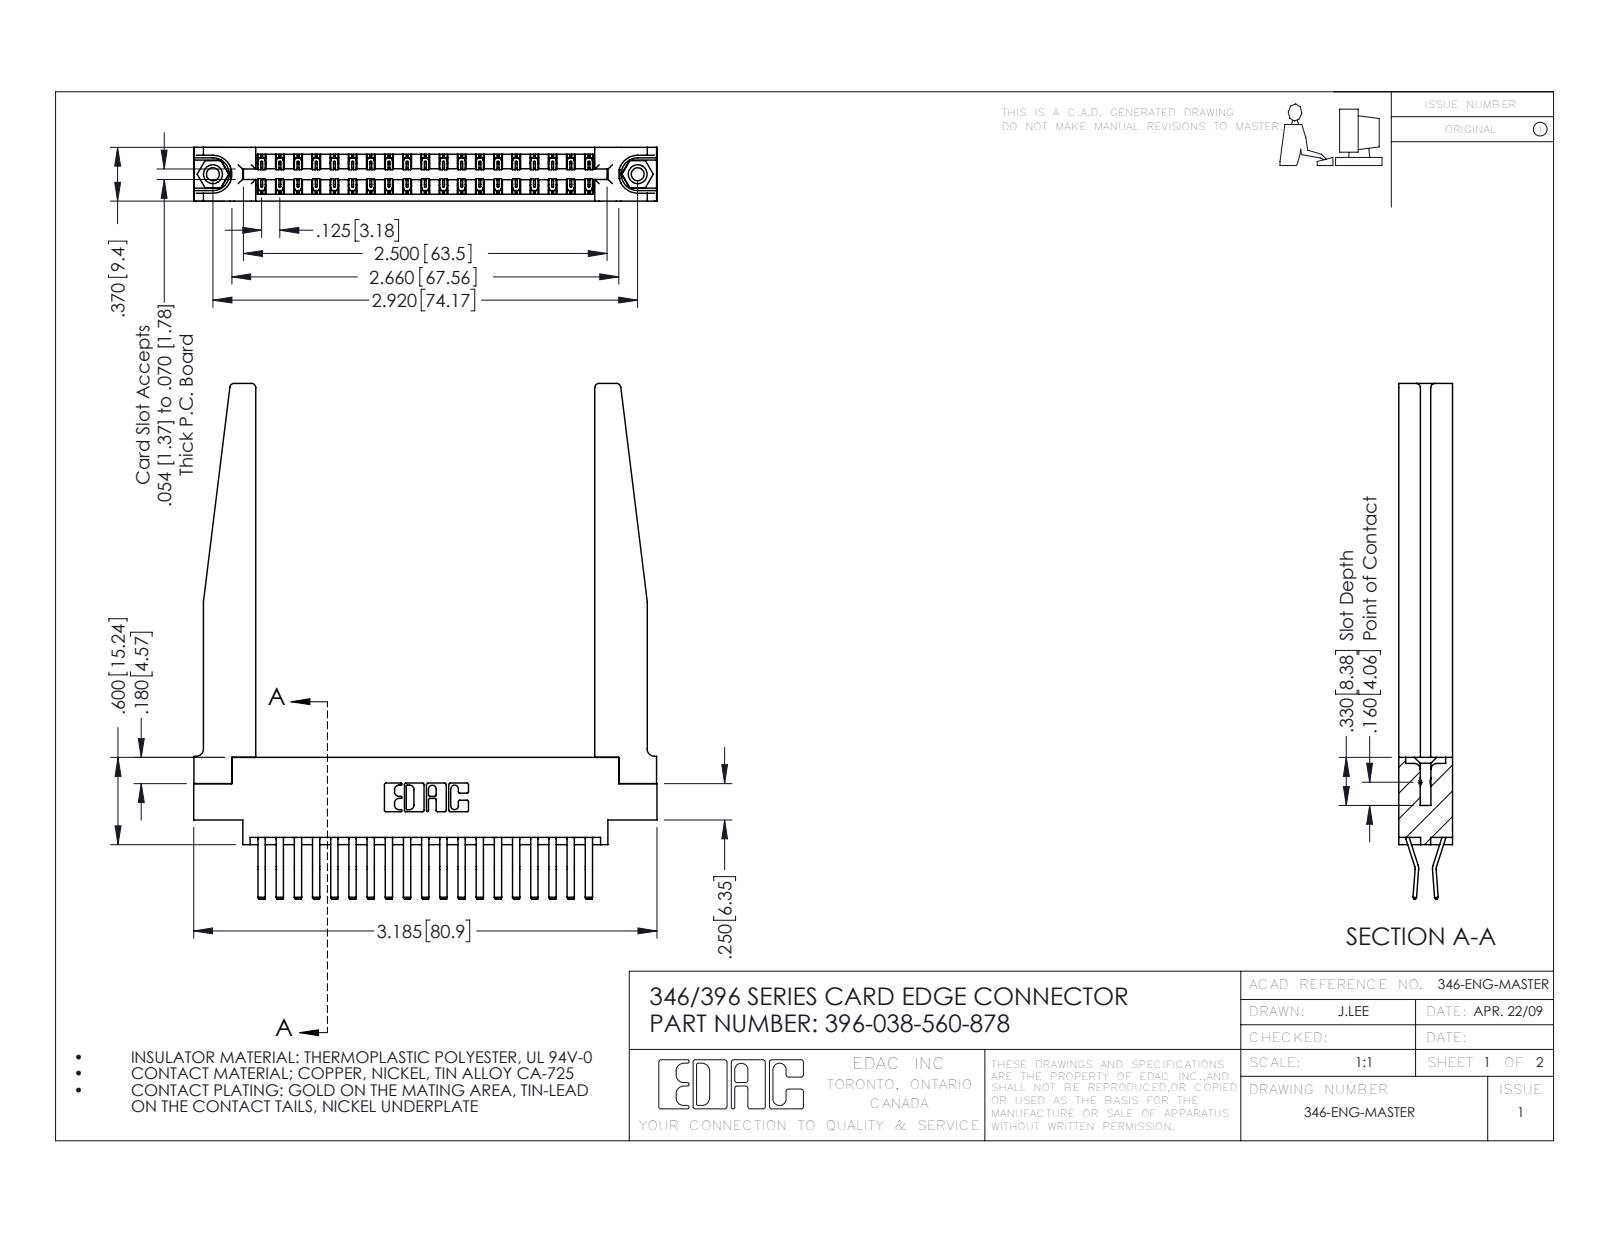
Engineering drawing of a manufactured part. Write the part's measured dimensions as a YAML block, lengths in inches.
part_name: "345-292-001_560 Tail; 396-038-560-878; 346-220-078_345-220-078; 346 Part_0.170 Offset - 0.156 Dia-TH (+1 more)"
step_written_by: "SolidWorks 2016 (CONFIG_CONTROL_DESIGN)"
units: inches
bodies: {solids: 43, faces: 2412, planar: 1552, cylindrical: 808, other: 52}
overall_size: [3.545, 3.185, 0.37]
volume: 0.898
surface_area: 27.51
round_holes:
  - {diameter: 0.089, count: 2}
  - {diameter: 0.125, count: 2}
  - {diameter: 0.156, count: 2}
  - {diameter: 0.064, count: 1}
round_bosses_or_shafts:
  - {diameter: 0.155, count: 2}
partial_cylinders:
  - {radius: 0.006, count: 57}
  - {radius: 0.01, count: 22}
  - {radius: 0.03, count: 8}
  - {radius: 0.007, count: 6}
  - {radius: 0.031, count: 6}
  - {radius: 0.05, count: 4}
  - {radius: 0.026, count: 3}
  - {radius: 0.01, count: 2}
face_to_face_distances: [0.37, 0.048, 0.322, 0.072, 0.148, 0.15, 0.025, 0.25, 0.298, 0.275]
hole_center_spacings: [0.246, 2.713, 2.92]
